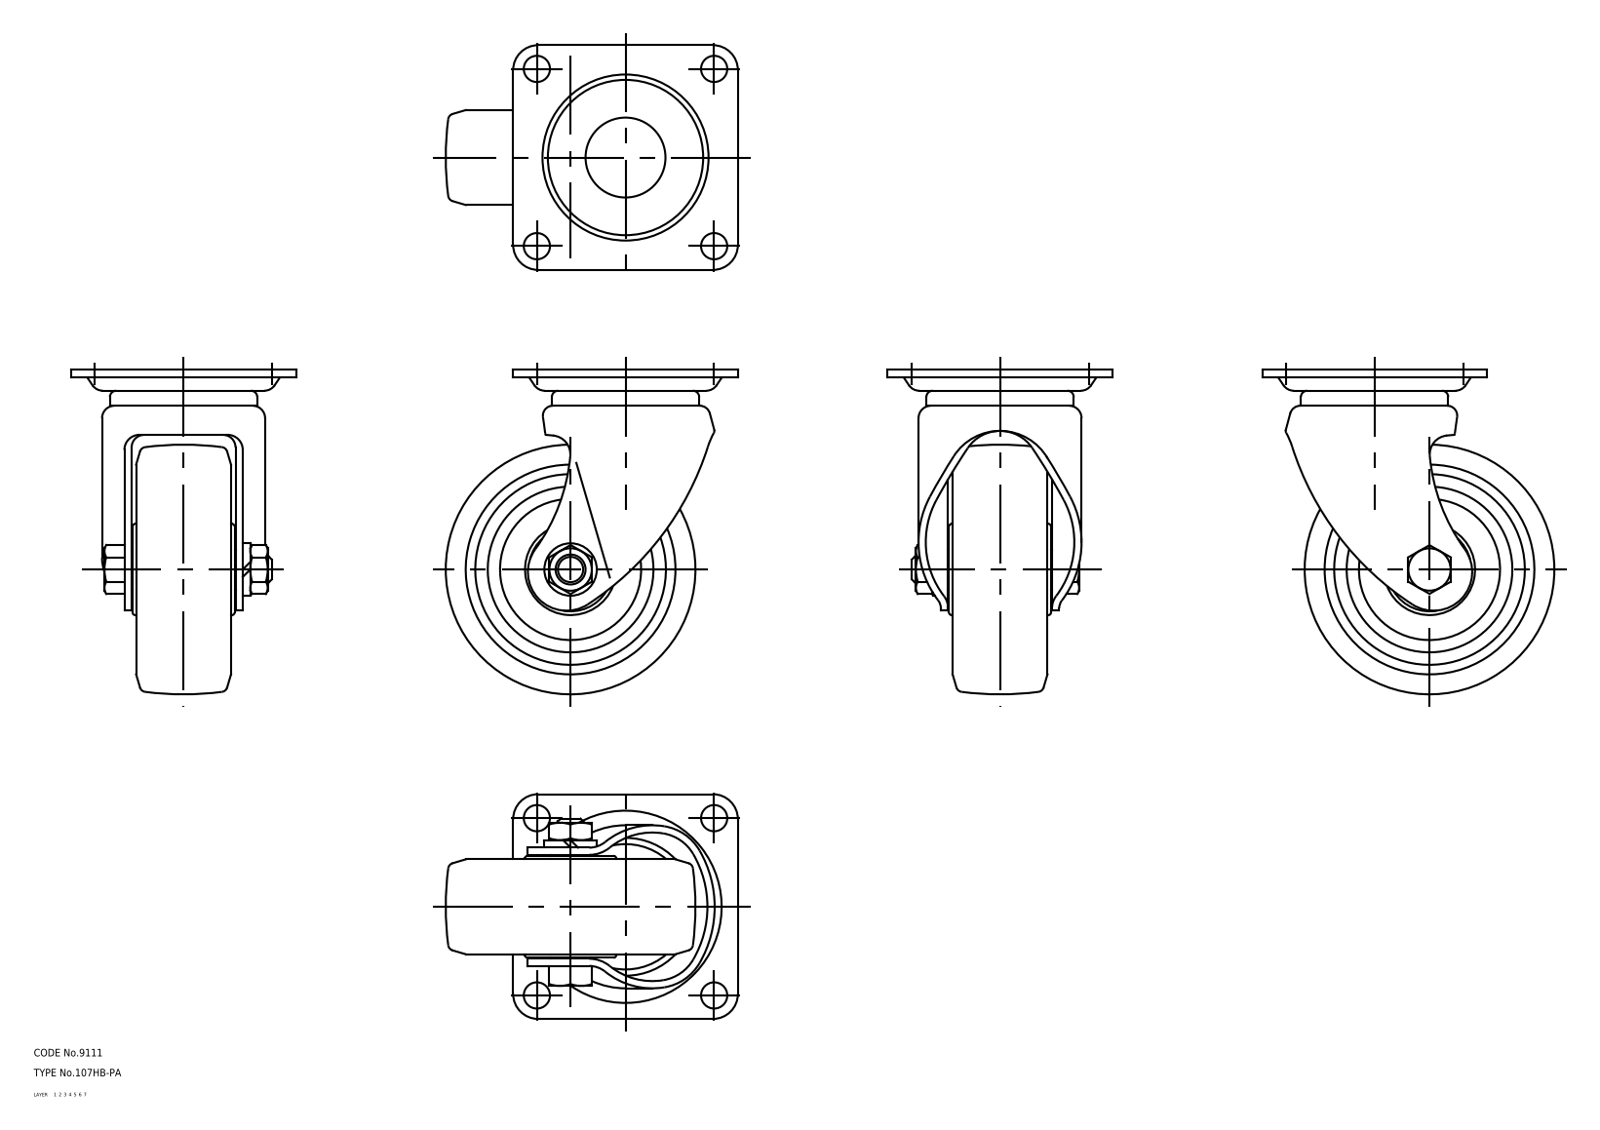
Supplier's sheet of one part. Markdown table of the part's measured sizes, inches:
| quantity | value |
| --- | --- |
| part name | 67125769; 67125782; 67125795; 67125808 (+1 more) |
| STEP written by | CADfix (AUTOMOTIVE_DESIGN) |
| units | inches |
| bodies | 5 solids, 238 faces (0 planar, 0 cylindrical, 238 other) |
| overall size | 5.118 × 4.606 × 3.543 |
| volume | 22.53 in³ |
| surface area | 127.7 in² |
